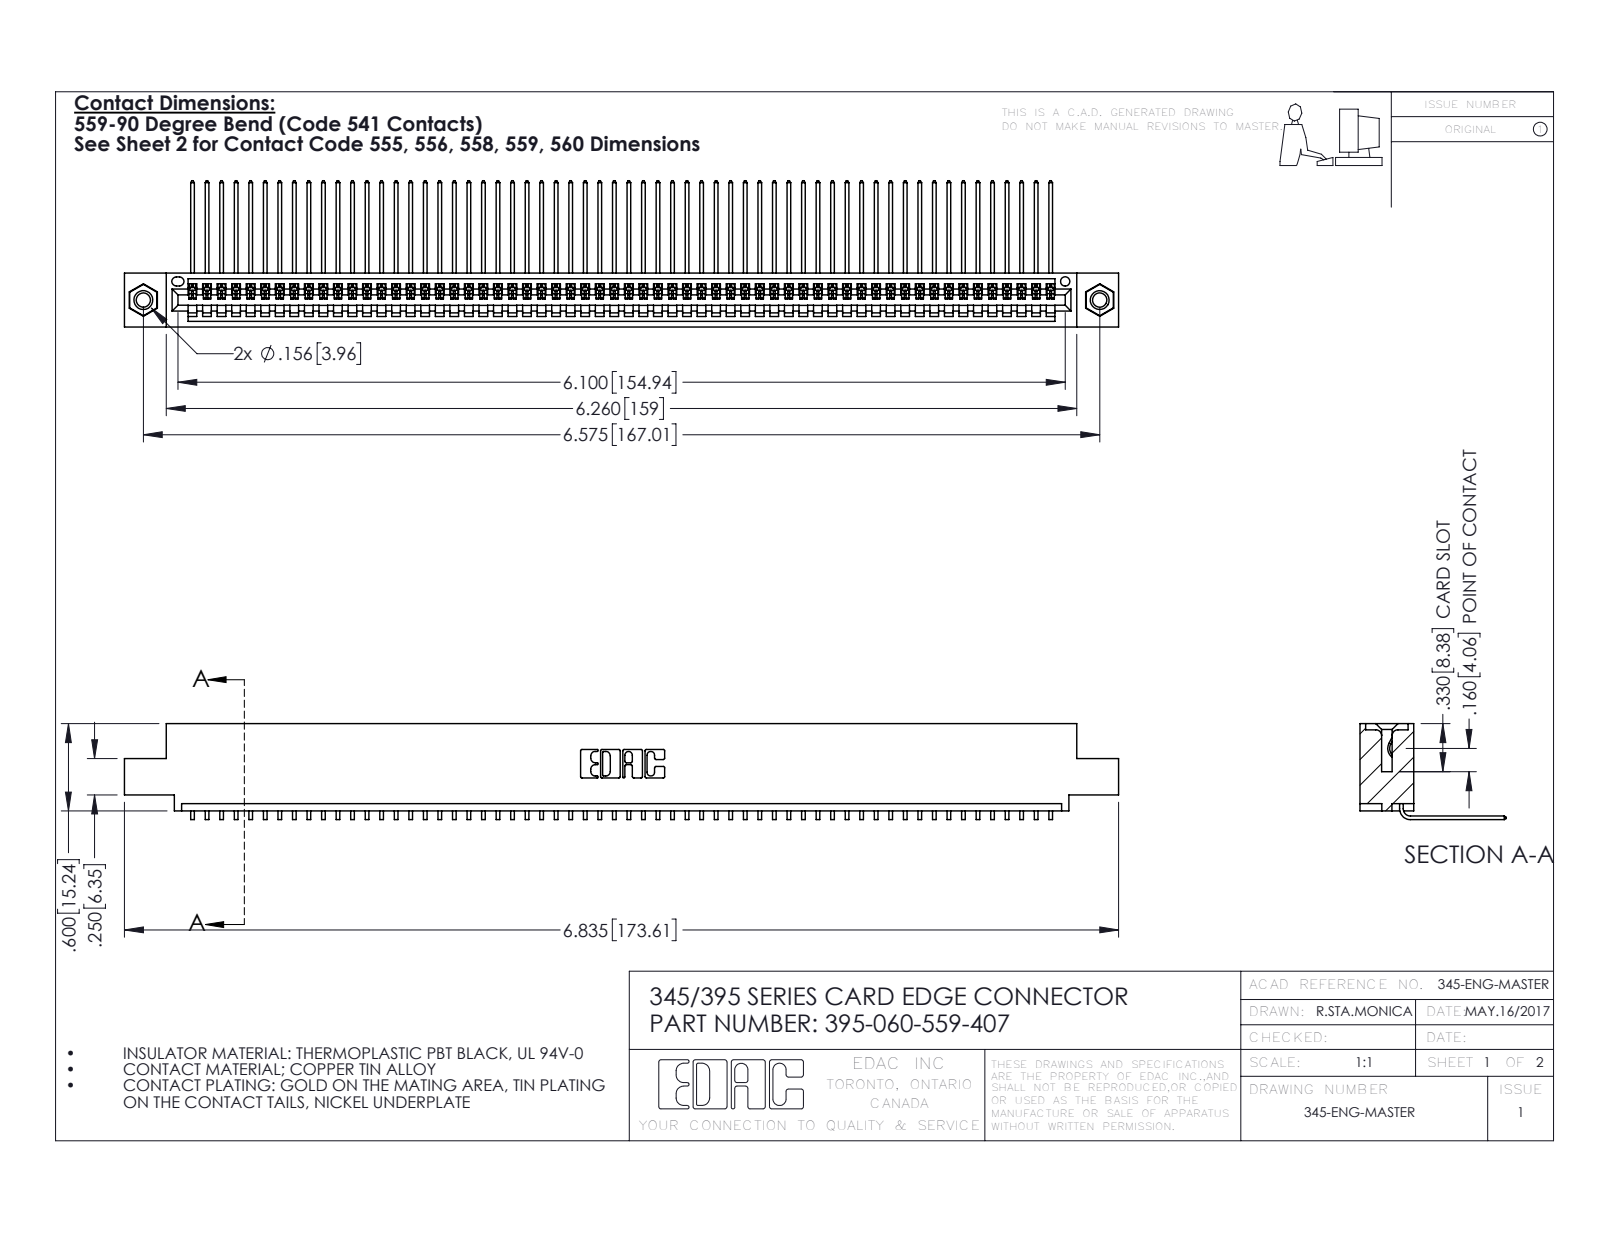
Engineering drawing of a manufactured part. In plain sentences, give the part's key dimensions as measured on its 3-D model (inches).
The part is named "345 Part_0.110 Offset - 0.156 Dia-TI; 345-250-001_345-250-005-103; 345-292-001_558 559 Tail - 1; 395-060-559-407". Its 3-D file was written by "SolidWorks 2016 (CONFIG_CONTROL_DESIGN)". It is 63 solids with 3790 faces: 2636 planar, 1138 cylindrical and 16 other. Overall it measures 6.835 by 1.005 by 0.659 inches. Its volume is 1.022 cubic inches and its surface area 36.88 square inches. Round holes: 2 of diameter 0.098, 2 of diameter 0.125, 2 of diameter 0.156, 1 of diameter 0.064. Round bosses or shafts: 2 of diameter 0.155. Partial cylindrical surfaces (rounded edges, fillets, slot ends): 120 of radius 0.006, 22 of radius 0.01, 6 of radius 0.007, 6 of radius 0.031, 3 of radius 0.026, 2 of radius 0.031, 2 of radius 0.04, 1 of radius 0.014. The main face-to-face distances are 0.072, 0.298, 0.37, 0.2, 0.098, 0.272, 0.025, 0.225, 0.149, 0.072. The hole center spacings are 0.27, 6.339, 6.575.
